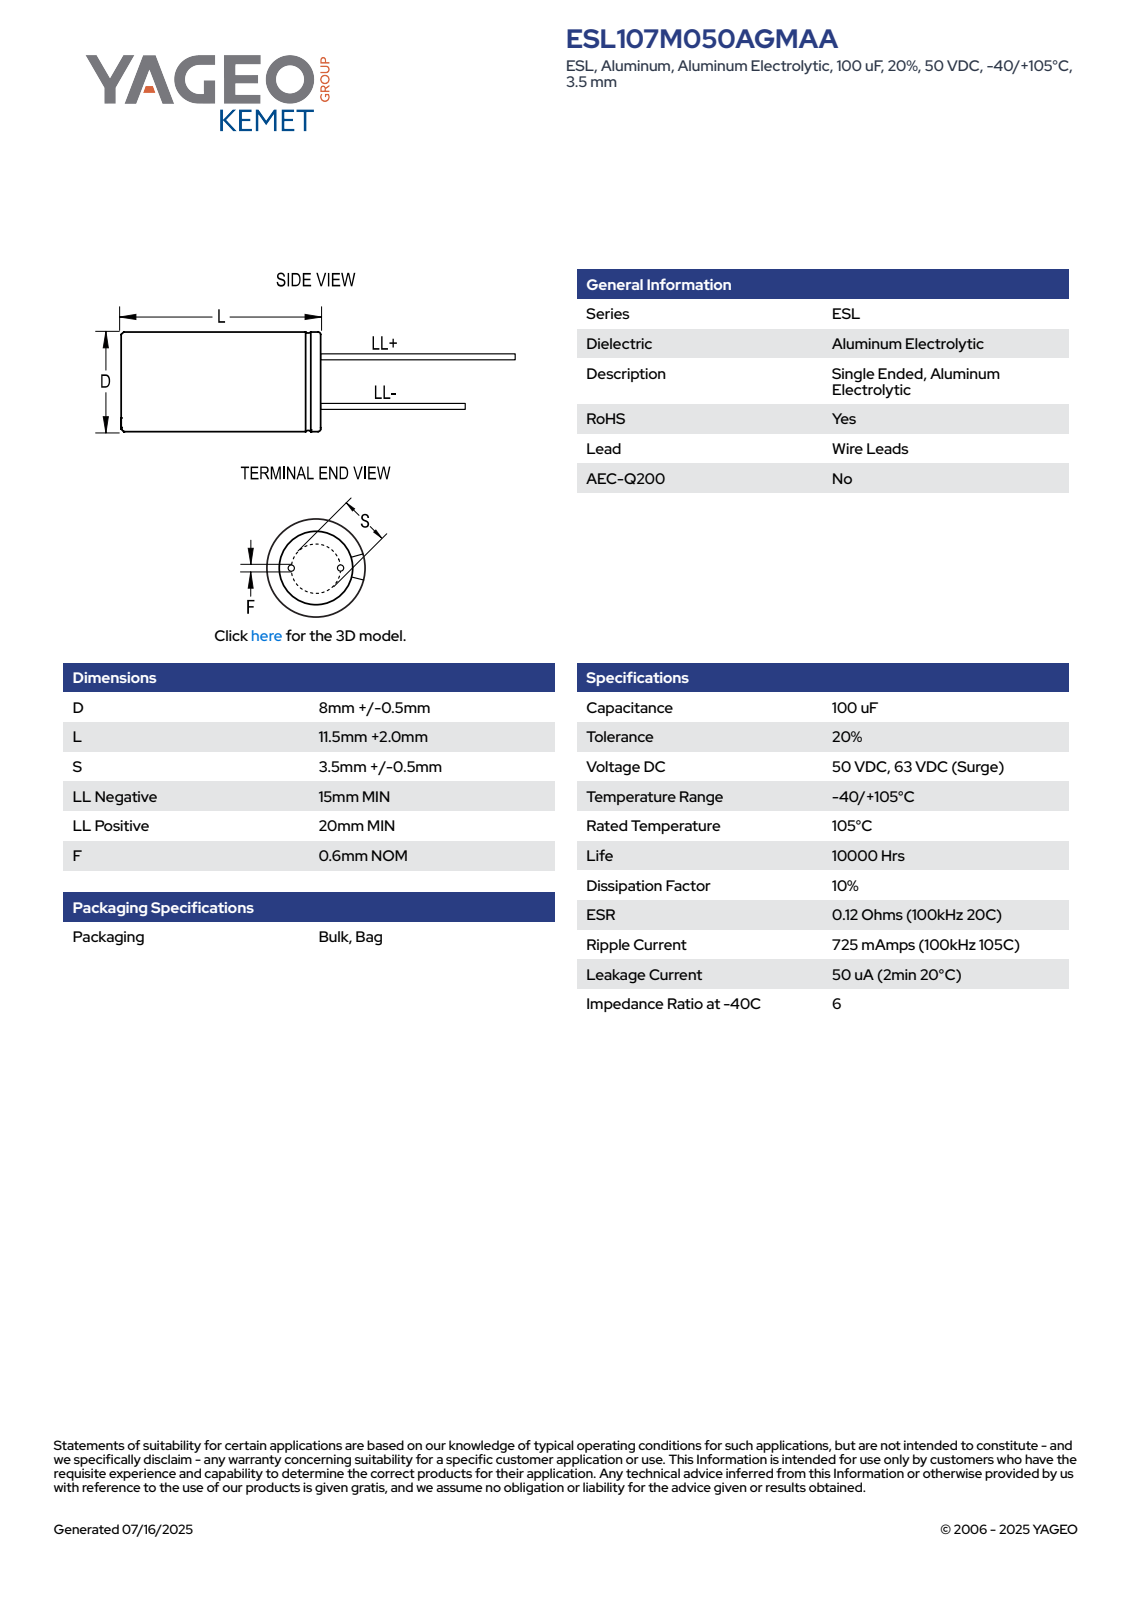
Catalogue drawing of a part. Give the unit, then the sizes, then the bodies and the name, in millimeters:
Units: millimetres
Overall size (bounding box): 33.51 × 8.5 × 8.5
Round bosses / shafts (diameter × count): ⌀0.6 ×2, ⌀8.5 ×1
Main face-to-face distances: 13.5, 13.51, 28.51, 33.51, 28.5, 33.5, 15, 20, 5, 1.15
Volume: 769 mm³ · Surface area: 556 mm²
Bodies: 4 solids, 75 faces (61 planar, 8 cylindrical, 6 other)
Part name (STEP PRODUCT): CAR_KLP_8X11.5_D8.5L13.5S3.5F0.6
STEP written by: SolidWorks 2014 (AUTOMOTIVE_DESIGN)
